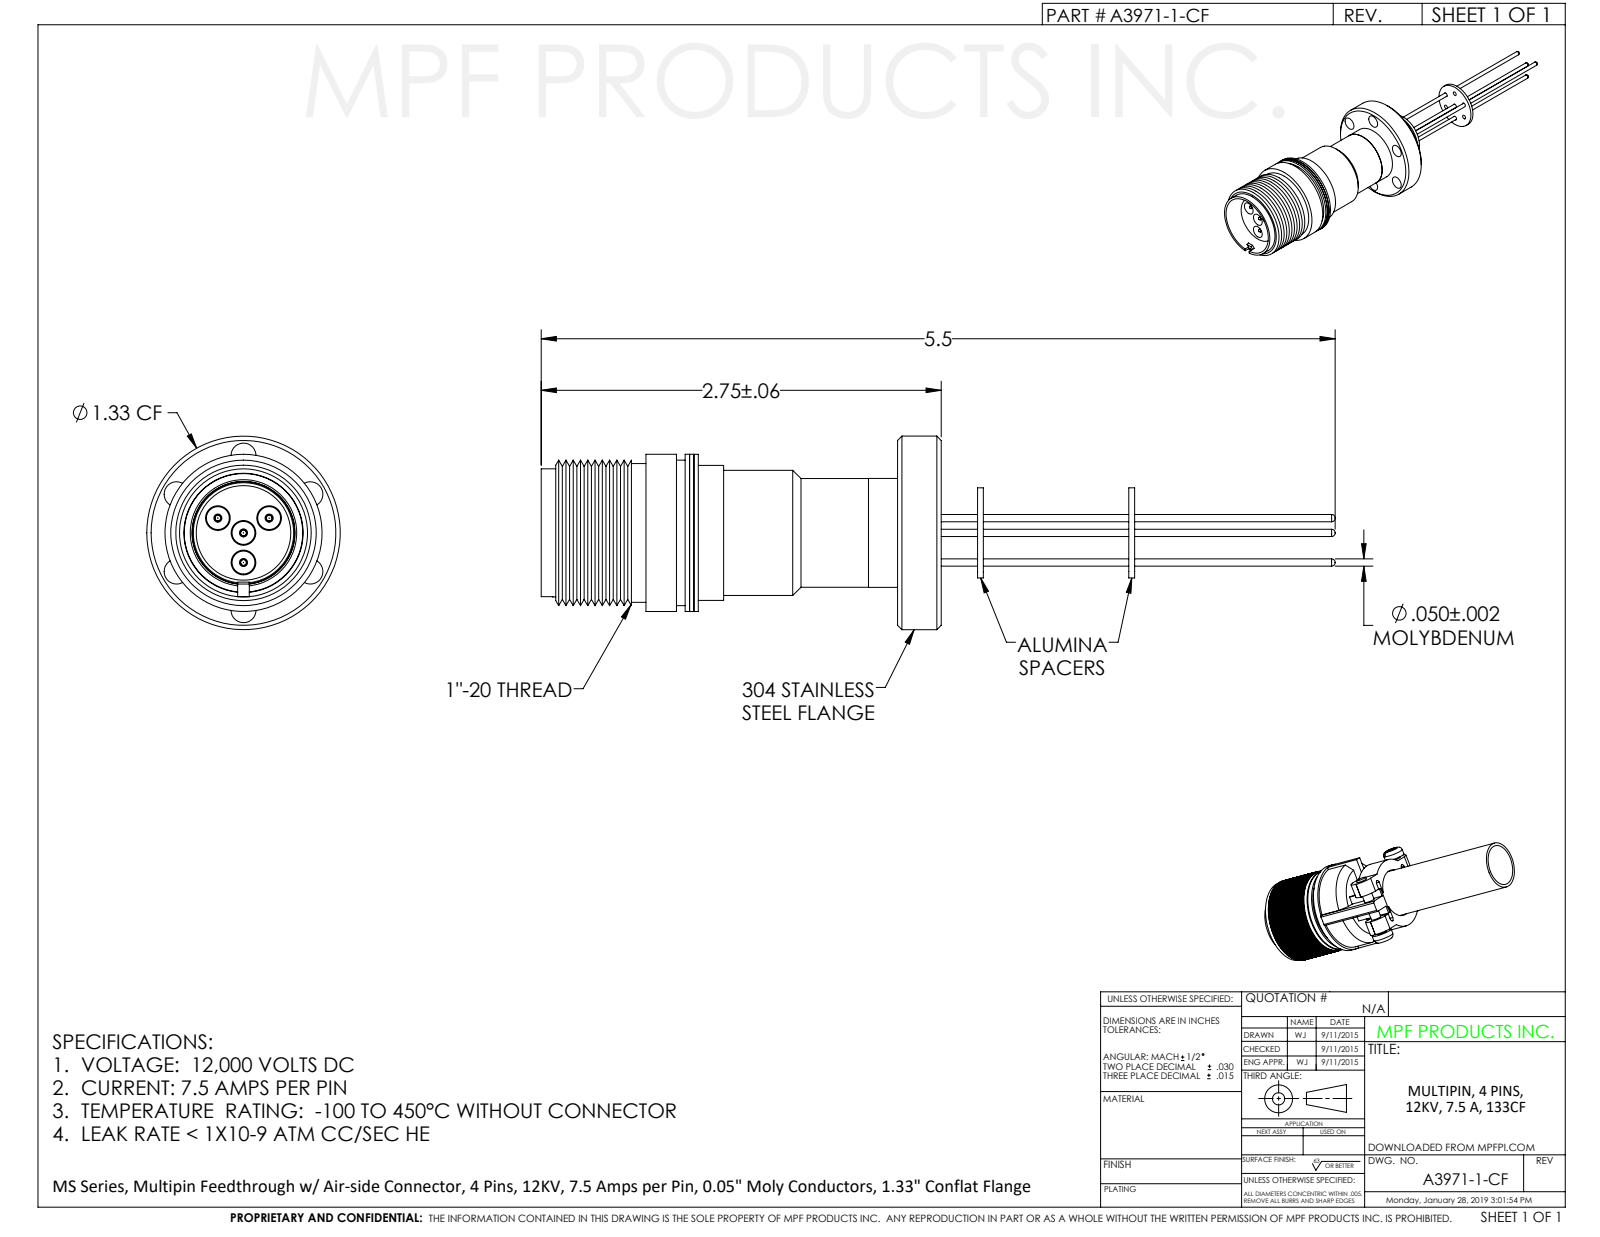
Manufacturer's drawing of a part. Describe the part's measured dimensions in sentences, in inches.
The part is named "A3971-1-CF". Its 3-D file was written by "SolidWorks 2012 (CONFIG_CONTROL_DESIGN)". It is 1 solid with 320 faces: 55 planar, 147 cylindrical and 118 other. Overall it measures 5.452 by 1.33 by 1.33 inches. Its volume is 1.199 cubic inches and its surface area 31.51 square inches. Round holes: 6 of diameter 0.172, 4 of diameter 0.042, 4 of diameter 0.056, 4 of diameter 0.152, 3 of diameter 0.036, 1 of diameter 0.63, 1 of diameter 0.687, 1 of diameter 0.725, 1 of diameter 0.791, 1 of diameter 0.8, 1 of diameter 0.82, 1 of diameter 0.845. Round bosses or shafts: 4 of diameter 0.14, 4 of diameter 0.05, 4 of diameter 0.04, 1 of diameter 1.33, 1 of diameter 1.08, 1 of diameter 1, 1 of diameter 0.954, 1 of diameter 0.928. The main face-to-face distances are 0.285, 1.5, 2.543, 0.758, 1.043, 1.571, 1.611, 2.583, 0.813, 0.853. The hole center spacings are 0.204, 0.531, 0.734, 0.92, 0.328, 0.352, 0.454, 0.474.
